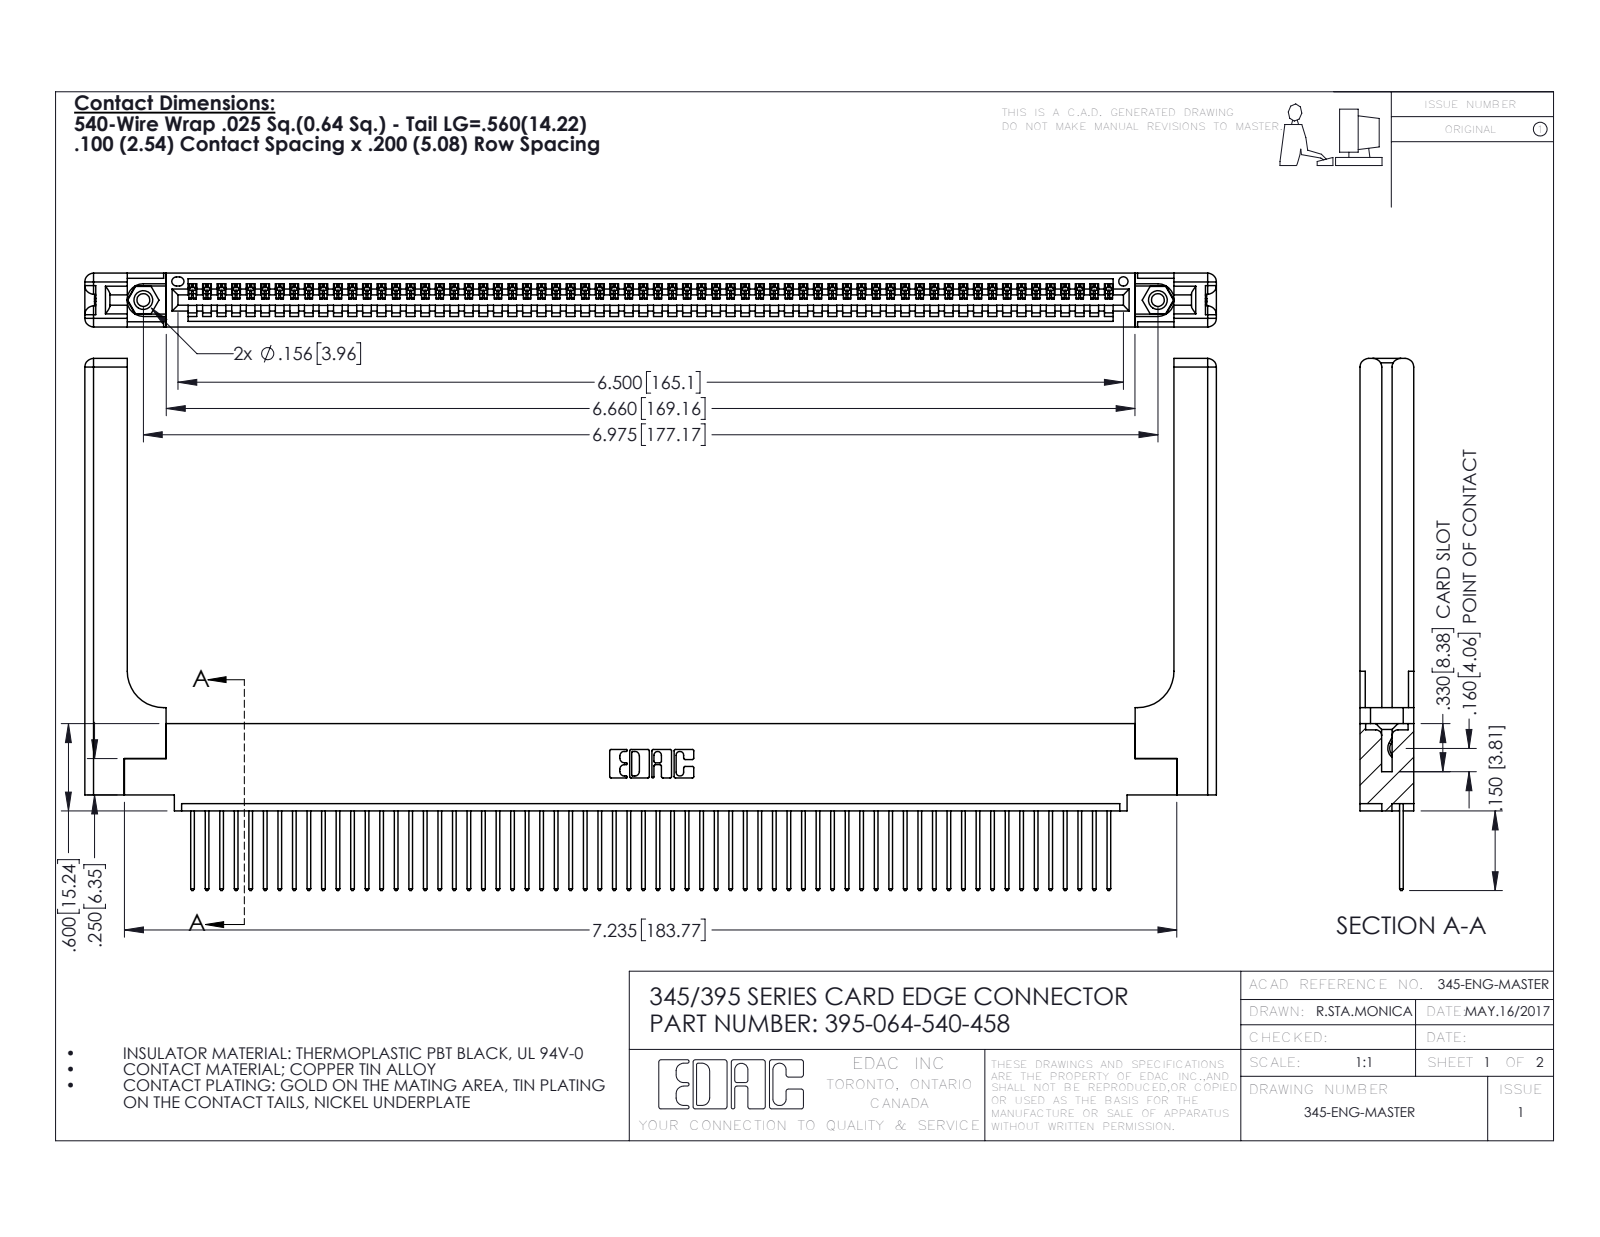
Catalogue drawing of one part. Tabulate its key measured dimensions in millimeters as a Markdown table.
| quantity | value |
| --- | --- |
| part name | 395-064-540-458; 345-220-058_345-220-058; 345-292-001_345-293-140; 345-250-001_345-250-001-102 (+1 more) |
| STEP written by | SolidWorks 2016 (CONFIG_CONTROL_DESIGN) |
| units | millimeters |
| bodies | 69 solids, 4098 faces (2792 planar, 1246 cylindrical, 60 other) |
| overall size | 197.6 × 92.9 × 9.4 |
| volume | 27 460 mm³ |
| surface area | 31 510 mm² |
| round holes (diameter × count) | 2.3 × 2, 3.2 × 2, 4 × 2, 1.6 × 1 |
| round bosses / shafts (diameter × count) | 3.9 × 2 |
| partial cylindrical surfaces (radius × count) | 0.2 × 128, 0.3 × 128, 0.3 × 22, 1.5 × 16, 0.2 × 6, 0.8 × 6, 0.7 × 3, 0.8 × 2 |
| main face-to-face distances | 1.8, 7.6, 9.4, 2.5, 6.9, 0.6, 5.1, 5.7, 3.8, 3.8 |
| hole center spacings | 6.9, 171.2, 177.2 |
